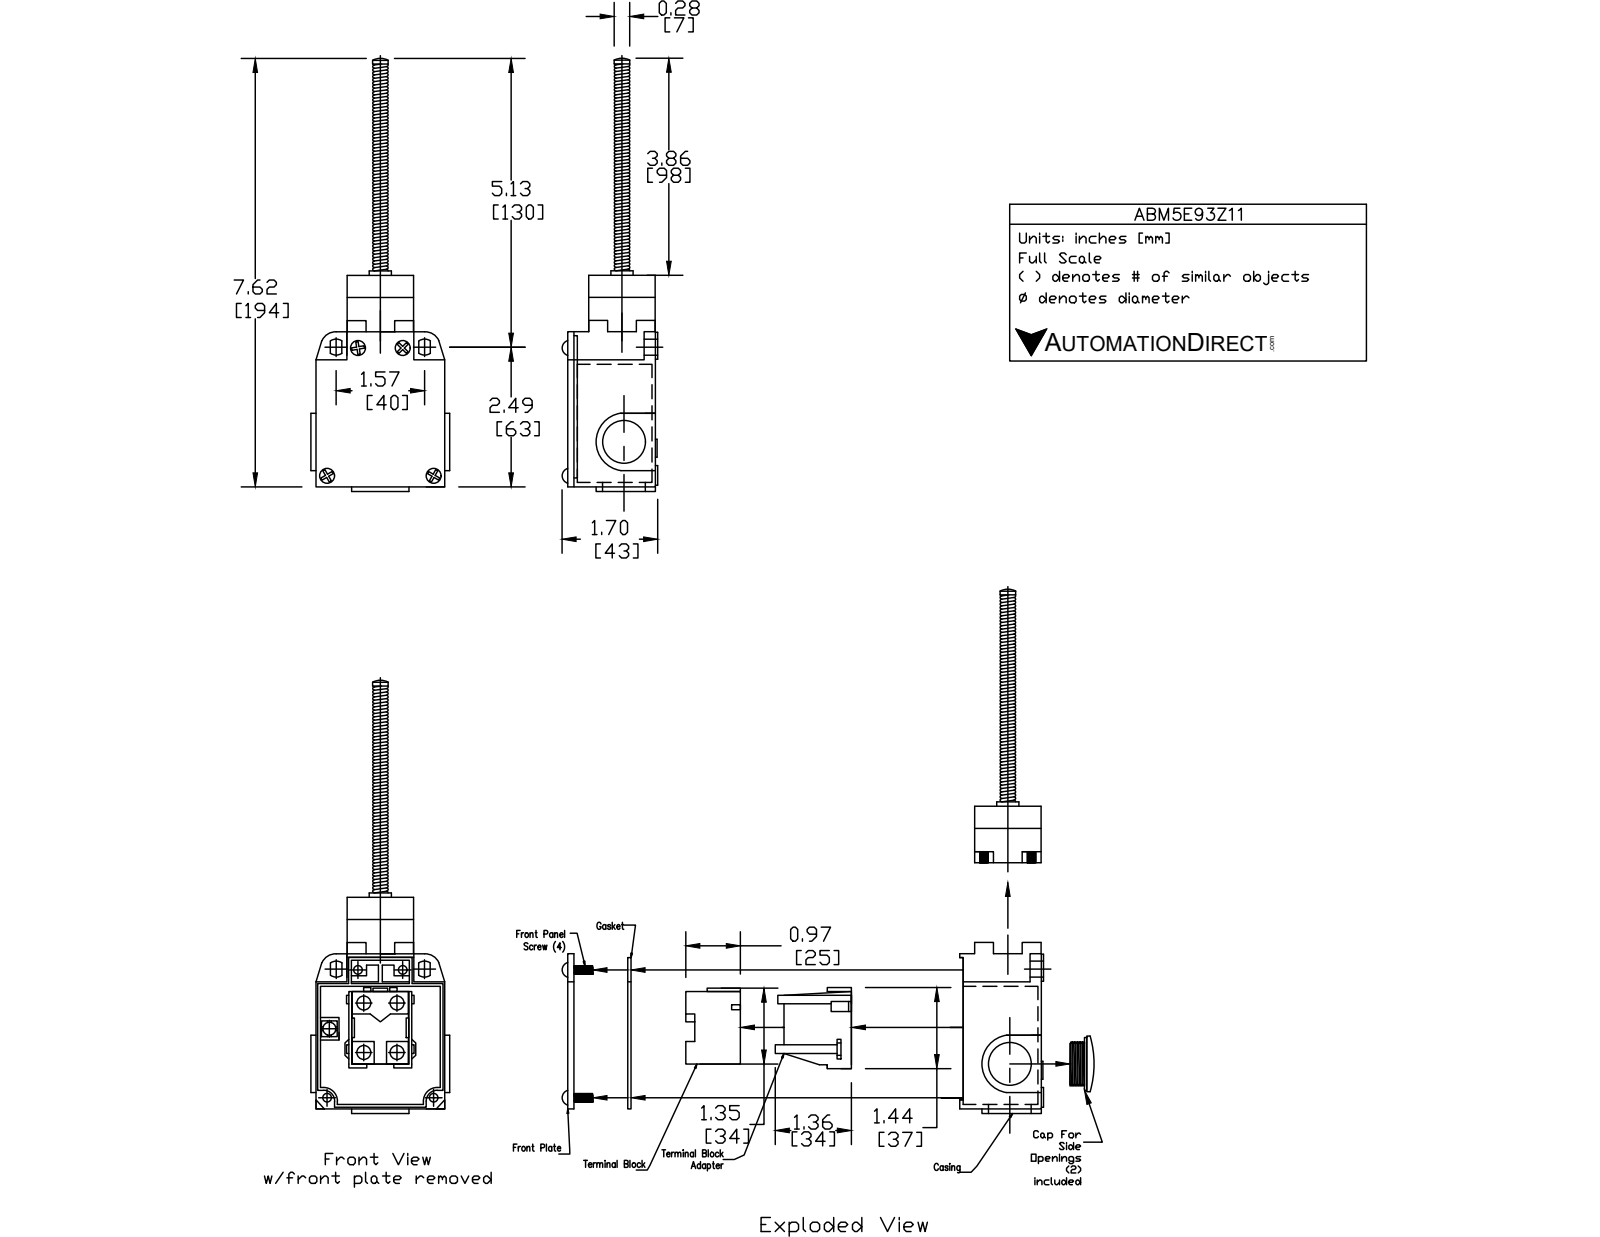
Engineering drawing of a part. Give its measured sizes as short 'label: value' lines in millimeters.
name: ABM5E93Z11
written by: SolidWorks 2017 (AUTOMOTIVE_DESIGN)
unit: mm
bodies: 3 solids, 196 faces (78 planar, 84 cylindrical, 34 other)
size: 198.3 × 43.3 × 40
volume: 130 500 mm³; area: 25 350 mm²
holes: 2× ⌀5.2, 1× ⌀17, 1× ⌀19, 1× ⌀20.5
bosses: 7× ⌀7, 4× ⌀10, 1× ⌀19, 1× ⌀11.7, 1× ⌀6.8
rounds: 16× R1.5, 4× R0.5, 4× R0.6, 4× R5, 2× R3.3, 1× R11.5, 1× R12
face distances: 40, 39.5, 30, 5, 76.5, 9.5, 35, 77, 0.5, 81.5
hole spacings: 1, 67.1
